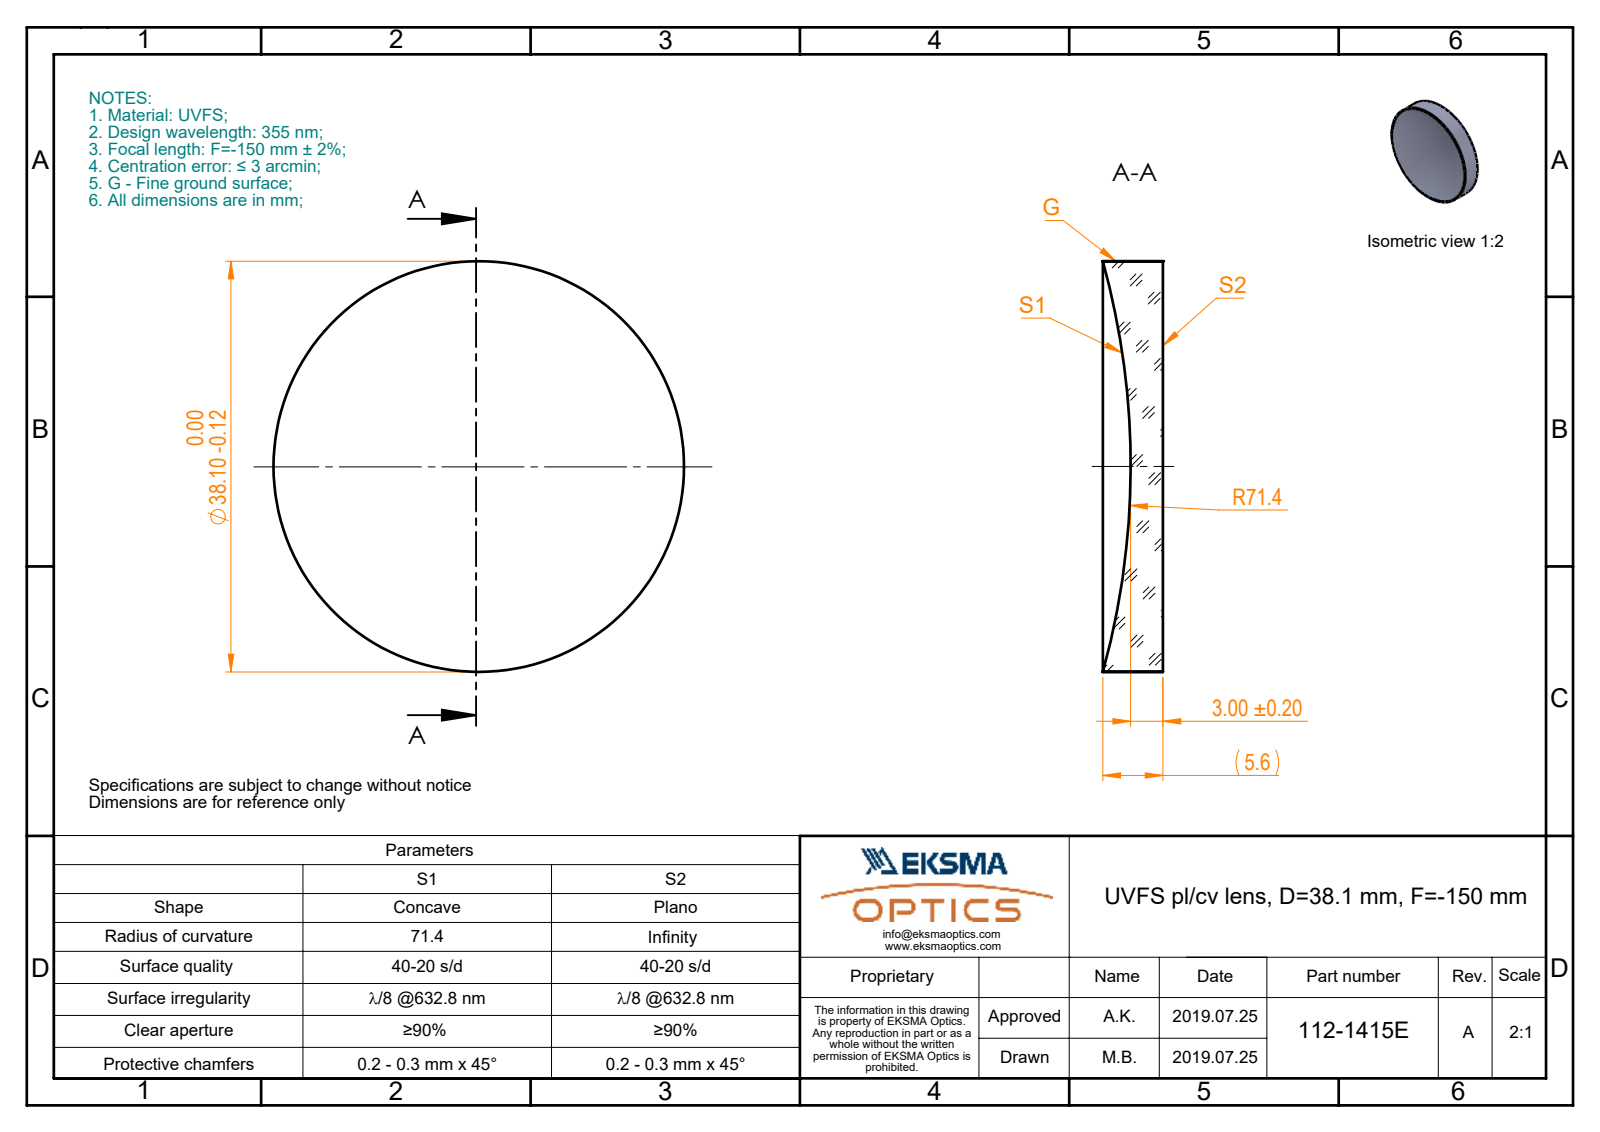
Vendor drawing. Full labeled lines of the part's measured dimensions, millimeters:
Part name (STEP PRODUCT): 112-1415E UVFS pl-cv 38.1 F-150
STEP written by: SolidWorks 2017 (CONFIG_CONTROL_DESIGN)
Units: millimetres
Bodies: 1 solid, 5 faces (1 planar, 2 cylindrical, 2 other)
Overall size (bounding box): 38.1 × 38.1 × 5.59
Volume: 4 886 mm³ · Surface area: 2 970 mm²
Round bosses / shafts (diameter × count): ⌀38.1 ×1
